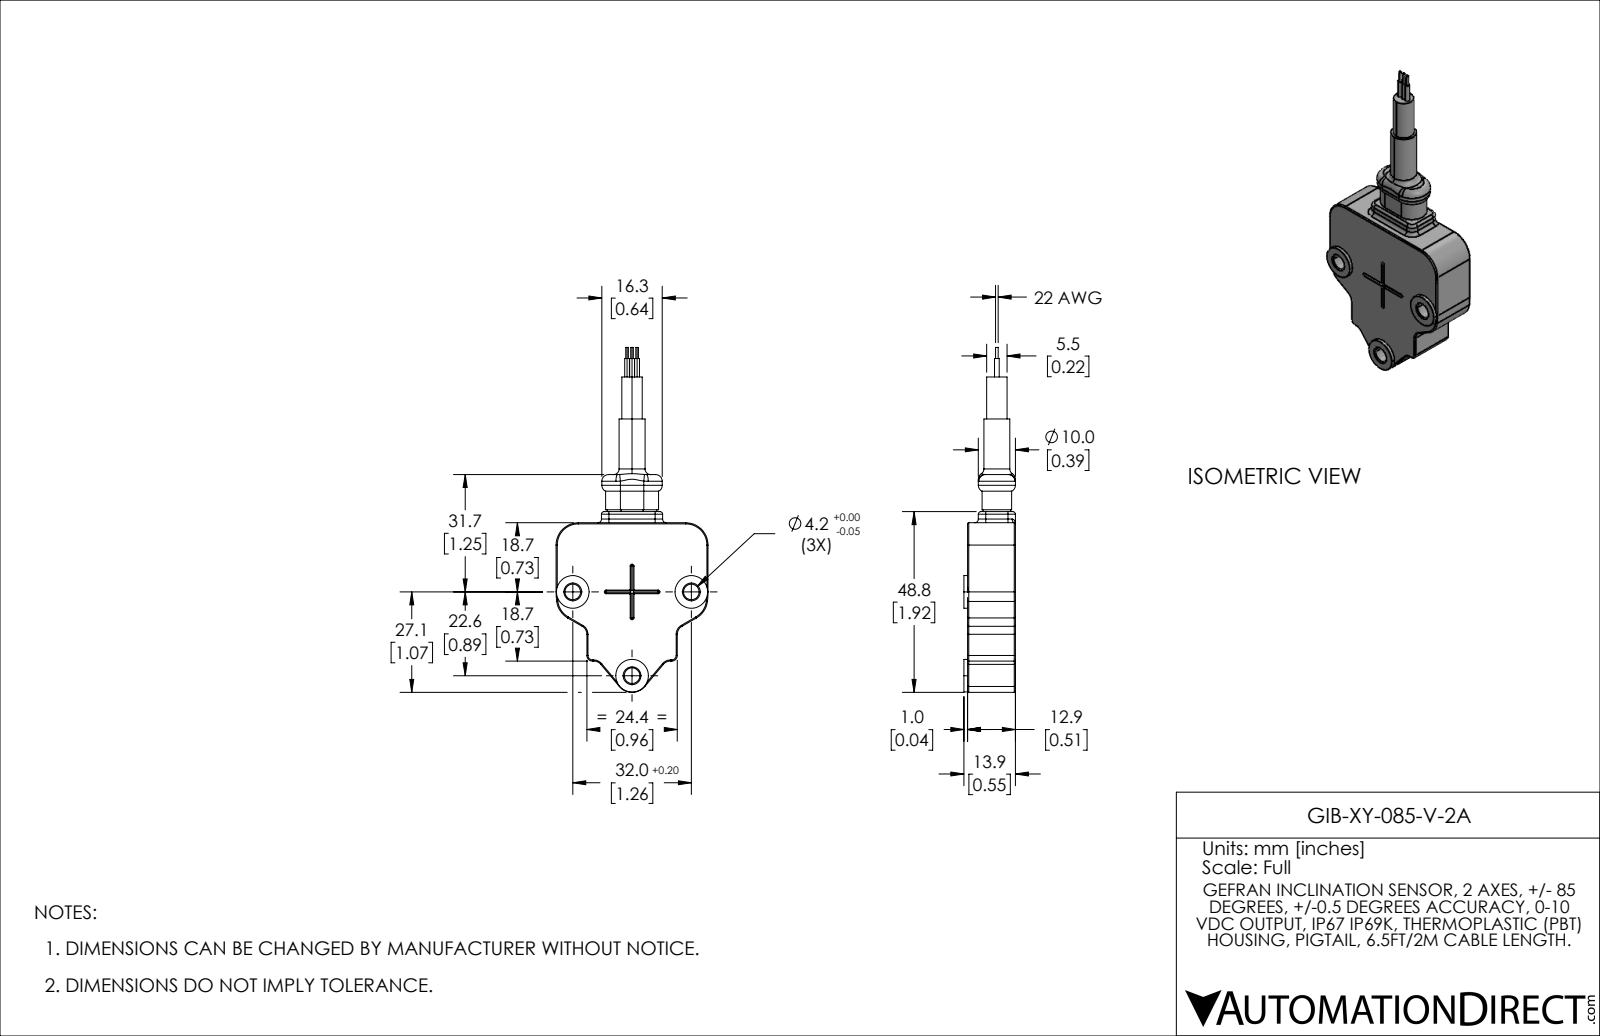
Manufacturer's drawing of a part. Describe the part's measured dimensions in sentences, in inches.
The part is named "GIB-XY-085-V-2A". Its 3-D file was written by "SolidWorks 2021 (AUTOMOTIVE_DESIGN)". It is 1 solid with 201 faces: 47 planar, 87 cylindrical and 67 other. Overall it measures 3.663 by 1.614 by 0.547 inches. Its volume is 1.246 cubic inches and its surface area 9.975 square inches. Round holes: 3 of diameter 0.165. Round bosses or shafts: 3 of diameter 0.346, 3 of diameter 0.051, 3 of diameter 0.028, 1 of diameter 0.276, 1 of diameter 0.217. Partial cylindrical surfaces (rounded edges, fillets, slot ends): 20 of radius 0.012, 4 of radius 0.008, 4 of radius 0.028, 4 of radius 0.079, 4 of radius 0.098, 4 of radius 0.236, 3 of radius 0.039, 2 of radius 0.059. The main face-to-face distances are 0.508, 0.039, 1.614, 0.327, 1.287, 0.547, 0.961, 0.354, 0.154, 0.118. The hole center spacings are 1.09, 1.26.
